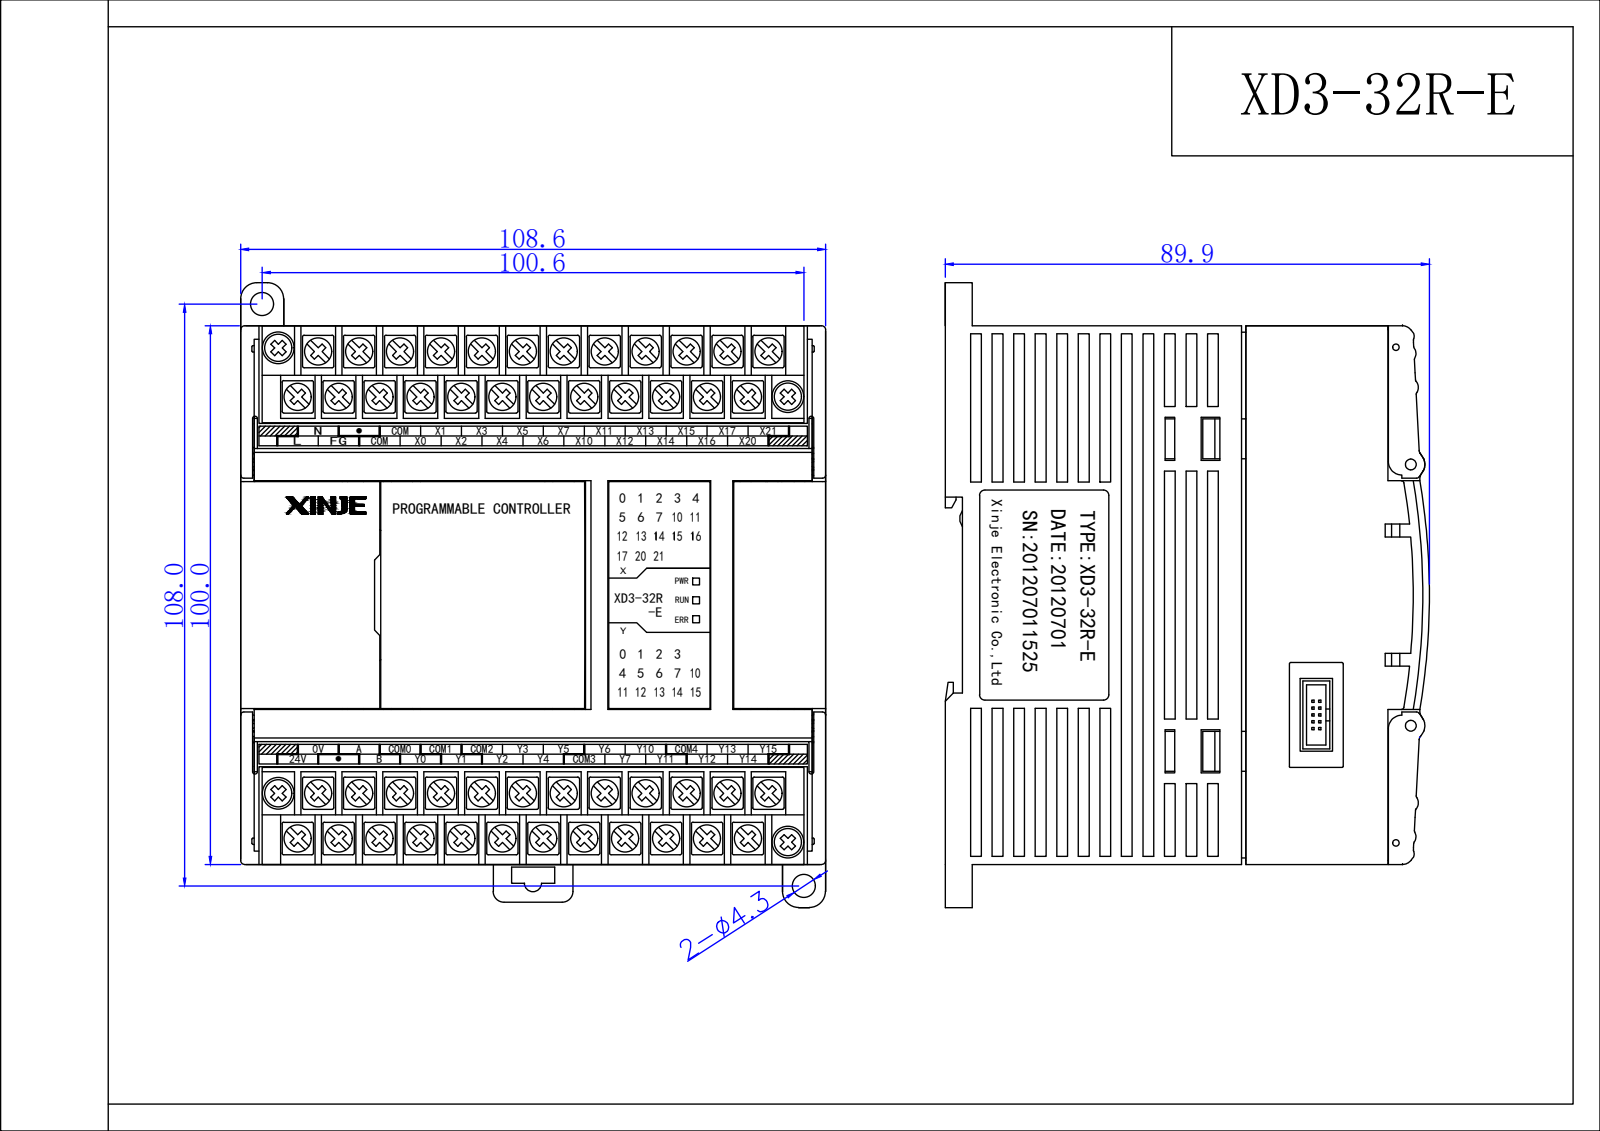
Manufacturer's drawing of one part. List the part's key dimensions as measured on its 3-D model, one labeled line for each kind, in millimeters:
STEP written by: ST-DEVELOPER v16.5 (CONFIG_CONTROL_DESIGN)
Units: millimetres
Bodies: 1 solid, 4579 faces (3017 planar, 1134 cylindrical, 428 other)
Overall size (bounding box): 137.37 × 116 × 108.66
Volume: 881 405 mm³ · Surface area: 97 605 mm²
Round holes (diameter × count): ⌀3.45 ×48, ⌀4.3 ×2
Round bosses / shafts (diameter × count): ⌀5.4 ×52, ⌀3 ×48, ⌀2.5 ×48
Partial cylindrical surfaces — rounded edges, fillets, slot ends (radius × count): R0.25 ×192, R0.2 ×102, R0.5 ×20, R0.75 ×8, R1 ×8, R0.1 ×4, R0.3 ×4, R0.45 ×4
Main face-to-face distances: 108.6, 3.2, 18.1, 81.9, 100, 108.3, 0.75, 99.25, 17.35, 81.15
Hole centre spacings: 7.6, 9.22, 15.2, 22.8, 30.4, 38, 45.6, 14.17
